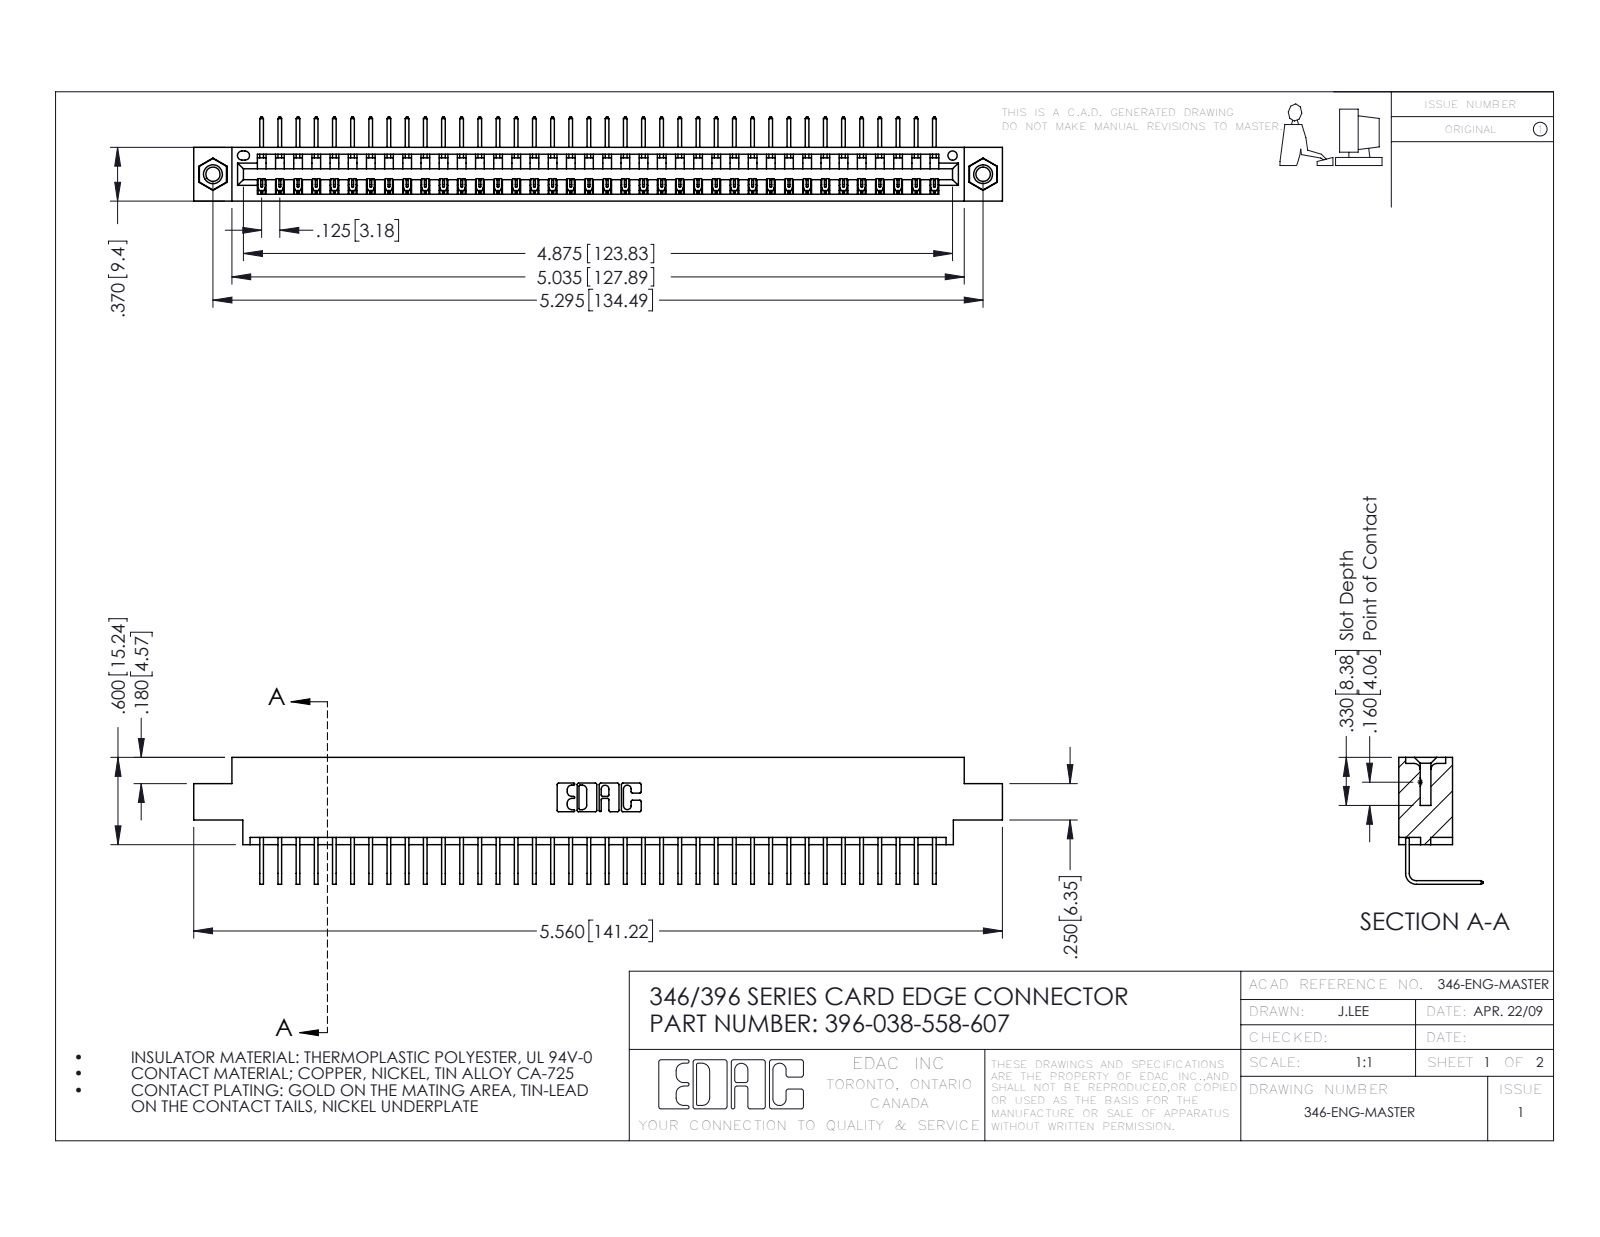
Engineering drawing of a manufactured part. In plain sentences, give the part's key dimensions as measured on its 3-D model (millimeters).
The part is named "346 Part_0.170 Offset - 0.156 Dia-TI; 396-038-558-607; 345-292-001_558 Tail - 2; 345-250-001_345-250-005-103". Its 3-D file was written by "SolidWorks 2016 (CONFIG_CONTROL_DESIGN)". It is 41 solids with 2466 faces: 1708 planar, 742 cylindrical and 16 other. Overall it measures 141.2 by 22.2 by 14.7 millimeters. Its volume is 13 500 cubic millimeters and its surface area 17 720 square millimeters. Round holes: 2 of diameter 2.5, 2 of diameter 3.2, 2 of diameter 4, 1 of diameter 1.6. Round bosses or shafts: 2 of diameter 3.9. Partial cylindrical surfaces (rounded edges, fillets, slot ends): 76 of radius 0.2, 22 of radius 0.3, 6 of radius 0.2, 6 of radius 0.8, 3 of radius 0.7, 2 of radius 0.8, 2 of radius 1, 1 of radius 0.4. The main face-to-face distances are 8.2, 1.2, 9.4, 6.4, 7.6, 0.6, 1.8, 5.6, 3.8, 2.5. The hole center spacings are 6.2, 129.2, 134.5.
